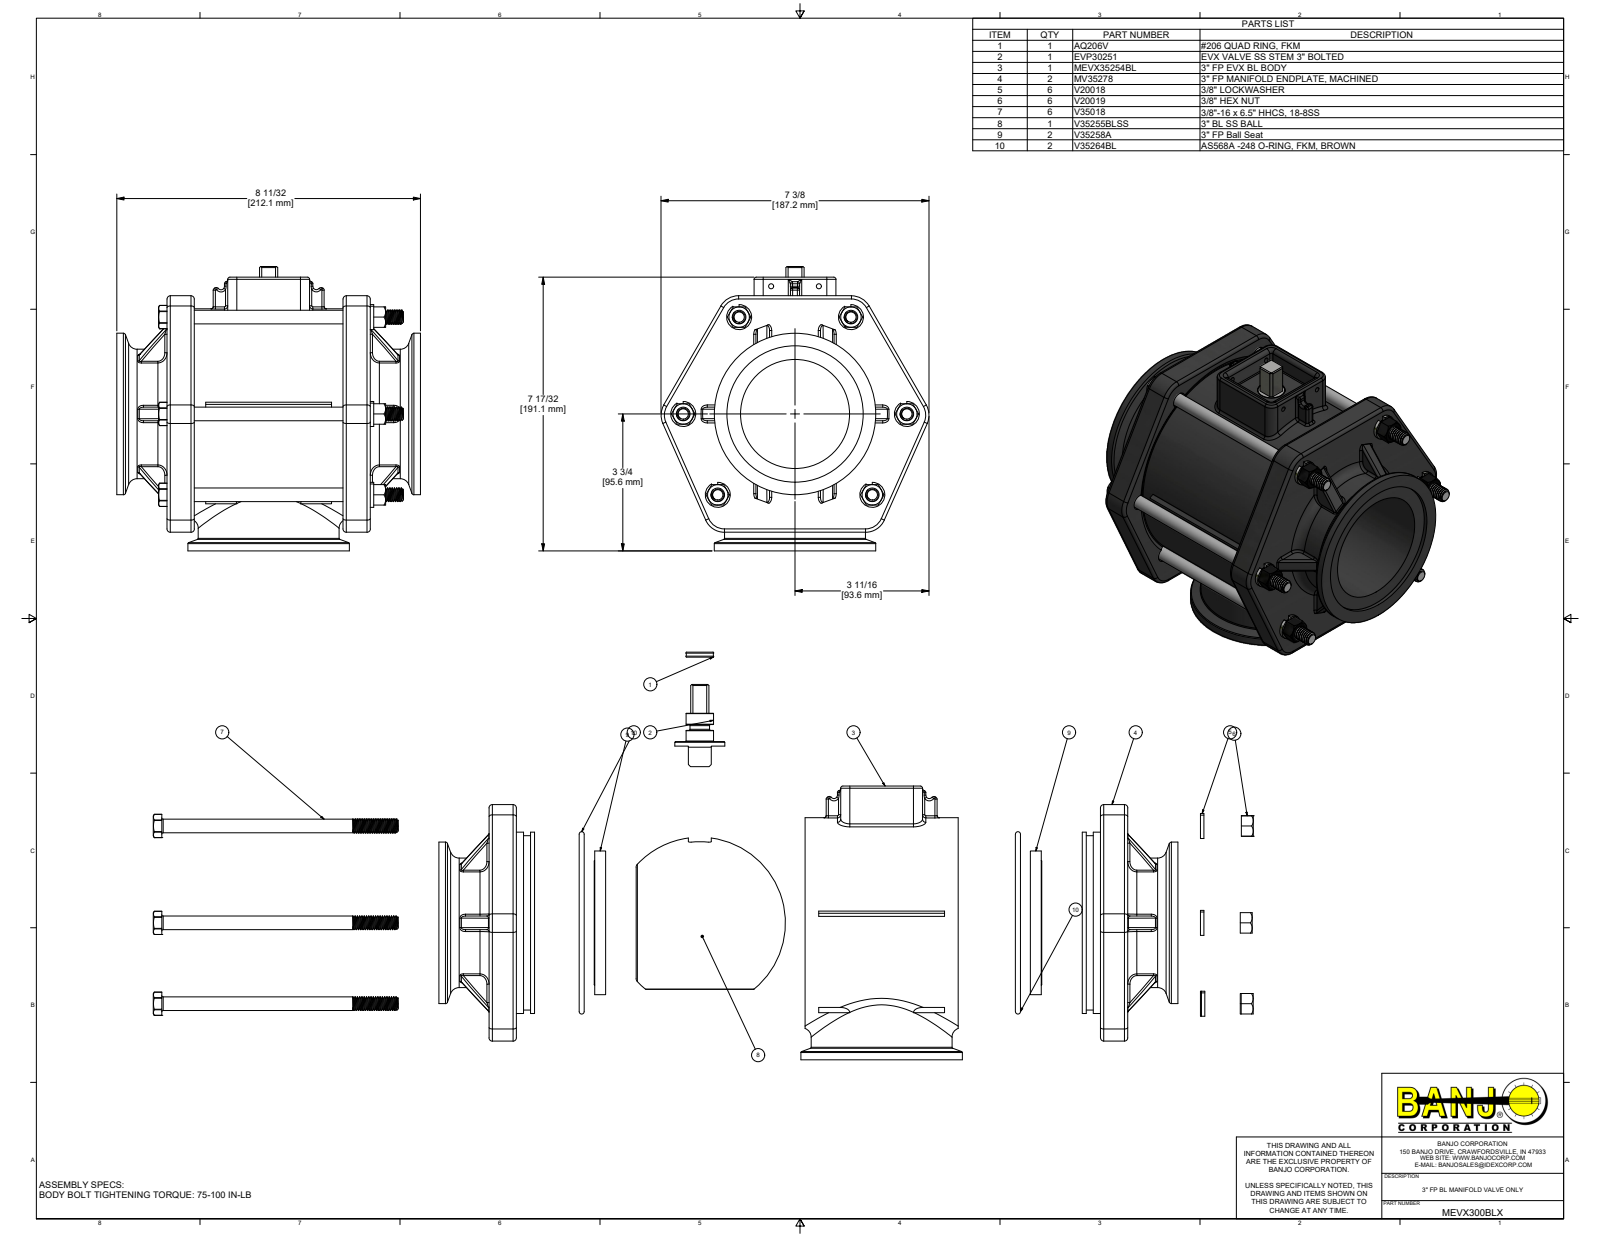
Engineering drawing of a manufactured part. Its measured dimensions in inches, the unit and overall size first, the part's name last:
Units: inches
Overall size (bounding box): 8.35 × 7.819 × 7.37
Round holes (diameter × count): ⌀0.44 ×8, ⌀0.307 ×6, ⌀0.385 ×6, ⌀0.135 ×2, ⌀2.92 ×2, ⌀3 ×2, ⌀0.76 ×1, ⌀1.437 ×1, ⌀3.1 ×1, ⌀3.212 ×1, ⌀3.25 ×1, ⌀3.73 ×1
Round bosses / shafts (diameter × count): ⌀0.687 ×6, ⌀0.375 ×6, ⌀0.294 ×6, ⌀4.44 ×2, ⌀5.78 ×1, ⌀4.985 ×1, ⌀4.793 ×1, ⌀3.875 ×1
Partial cylindrical surfaces — rounded edges, fillets, slot ends (radius × count): R0.06 ×58, R0.09 ×26, R0.078 ×8, R0.155 ×8, R0.32 ×6, R0.562 ×6, R0.03 ×4, R0.125 ×4
Main face-to-face distances: 0.69, 4.9, 5.59, 0.905, 4.685, 0.215, 3.995, 0.75, 4.84, 0.06
Hole centre spacings: 3.075, 2.417, 3.075, 4.263, 4.92, 5.655, 5.917, 1.222
Volume: 133.4 in³ · Surface area: 731.1 in²
Bodies: 28 solids, 1434 faces (295 planar, 625 cylindrical, 514 other)
Part name (STEP PRODUCT): MEVX300BLX; MEVX35254BL; MEVX35254BLX; MV35278 (+8 more)
STEP written by: Autodesk Inventor 2019 (AUTOMOTIVE_DESIGN)
